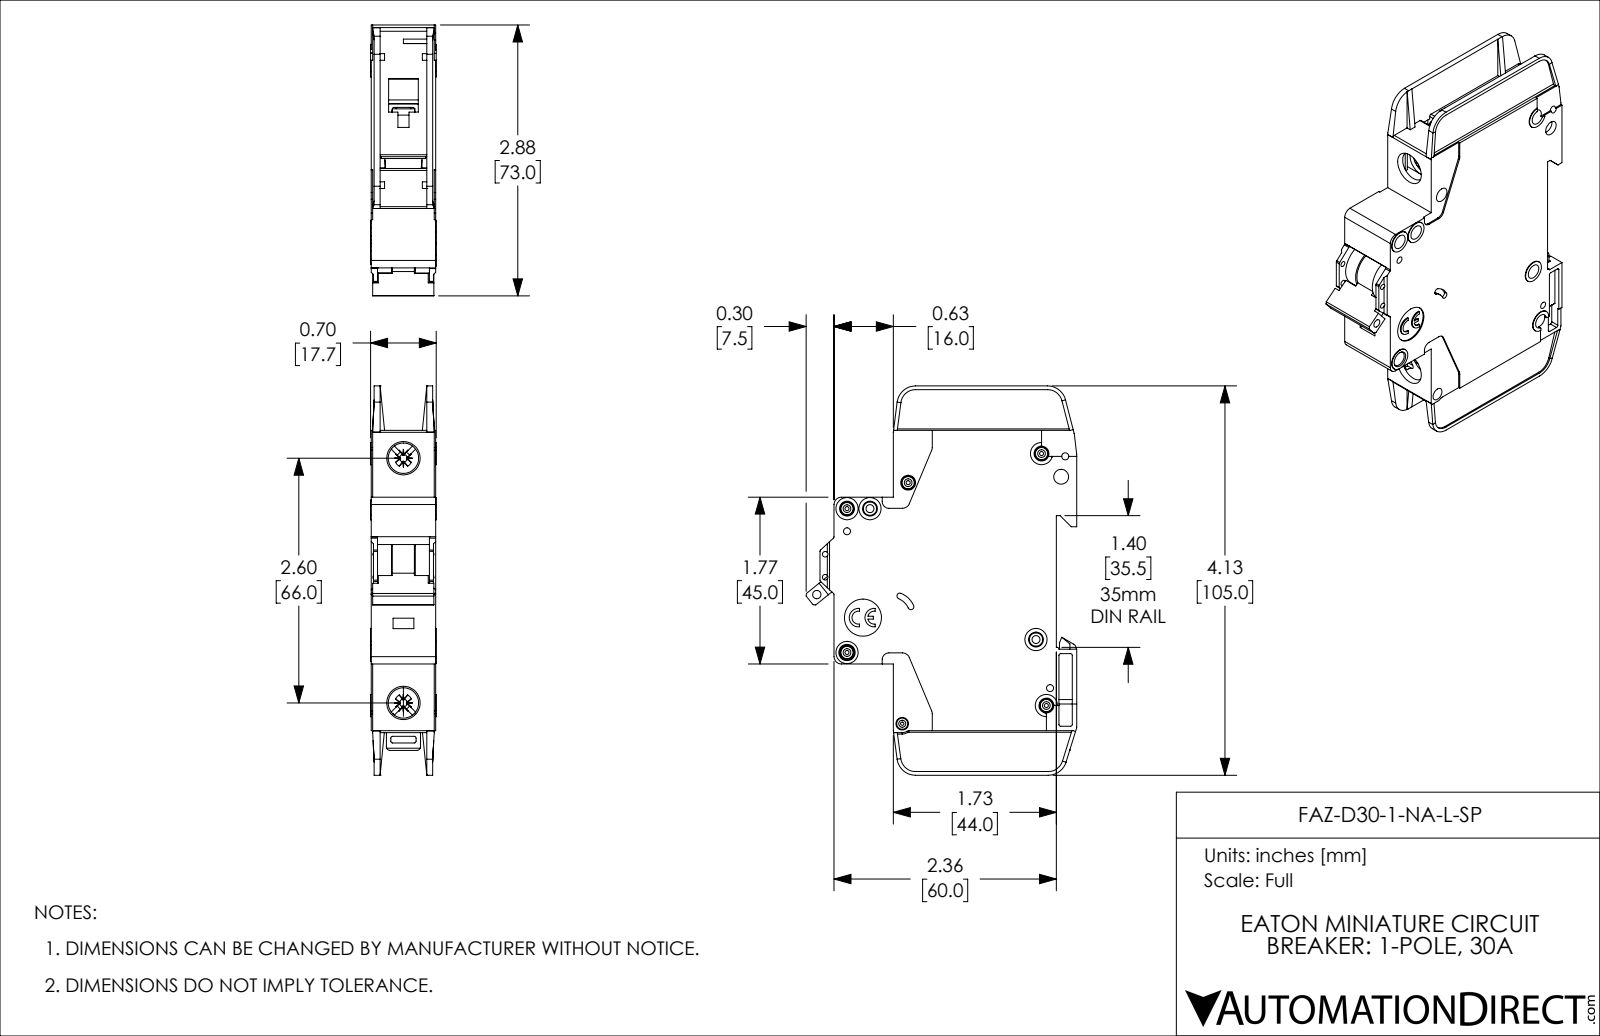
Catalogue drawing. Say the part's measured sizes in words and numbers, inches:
The part is named "FAZ-D30-1-NA-L-SP". Its 3-D file was written by "SolidWorks 2019 (AUTOMOTIVE_DESIGN)". It is 1 solid with 1127 faces: 671 planar, 357 cylindrical and 99 other. Overall it measures 4.134 by 2.876 by 0.697 inches. Its volume is 4.682 cubic inches and its surface area 41.01 square inches. Round holes: 8 of diameter 0.157, 5 of diameter 0.043, 4 of diameter 0.075, 2 of diameter 0.059, 2 of diameter 0.085, 2 of diameter 0.323, 1 of diameter 0.035, 1 of diameter 0.089, 1 of diameter 0.098, 1 of diameter 0.134, 1 of diameter 0.394. Round bosses or shafts: 5 of diameter 0.13, 4 of diameter 0.236, 2 of diameter 0.118, 1 of diameter 0.098. Partial cylindrical surfaces (rounded edges, fillets, slot ends): 42 of radius 0.02, 10 of radius 0.016, 10 of radius 0.039, 8 of radius 0.079, 5 of radius 0.197, 4 of radius 0.008, 4 of radius 0.026, 4 of radius 0.043. The main face-to-face distances are 0.047, 0.685, 0.591, 0.638, 0.094, 0.543, 0.016, 0.031, 0.496, 0.575. The hole center spacings are 0.244, 0.537, 0.87, 0.189, 0.199, 0.204, 0.221, 0.24.
